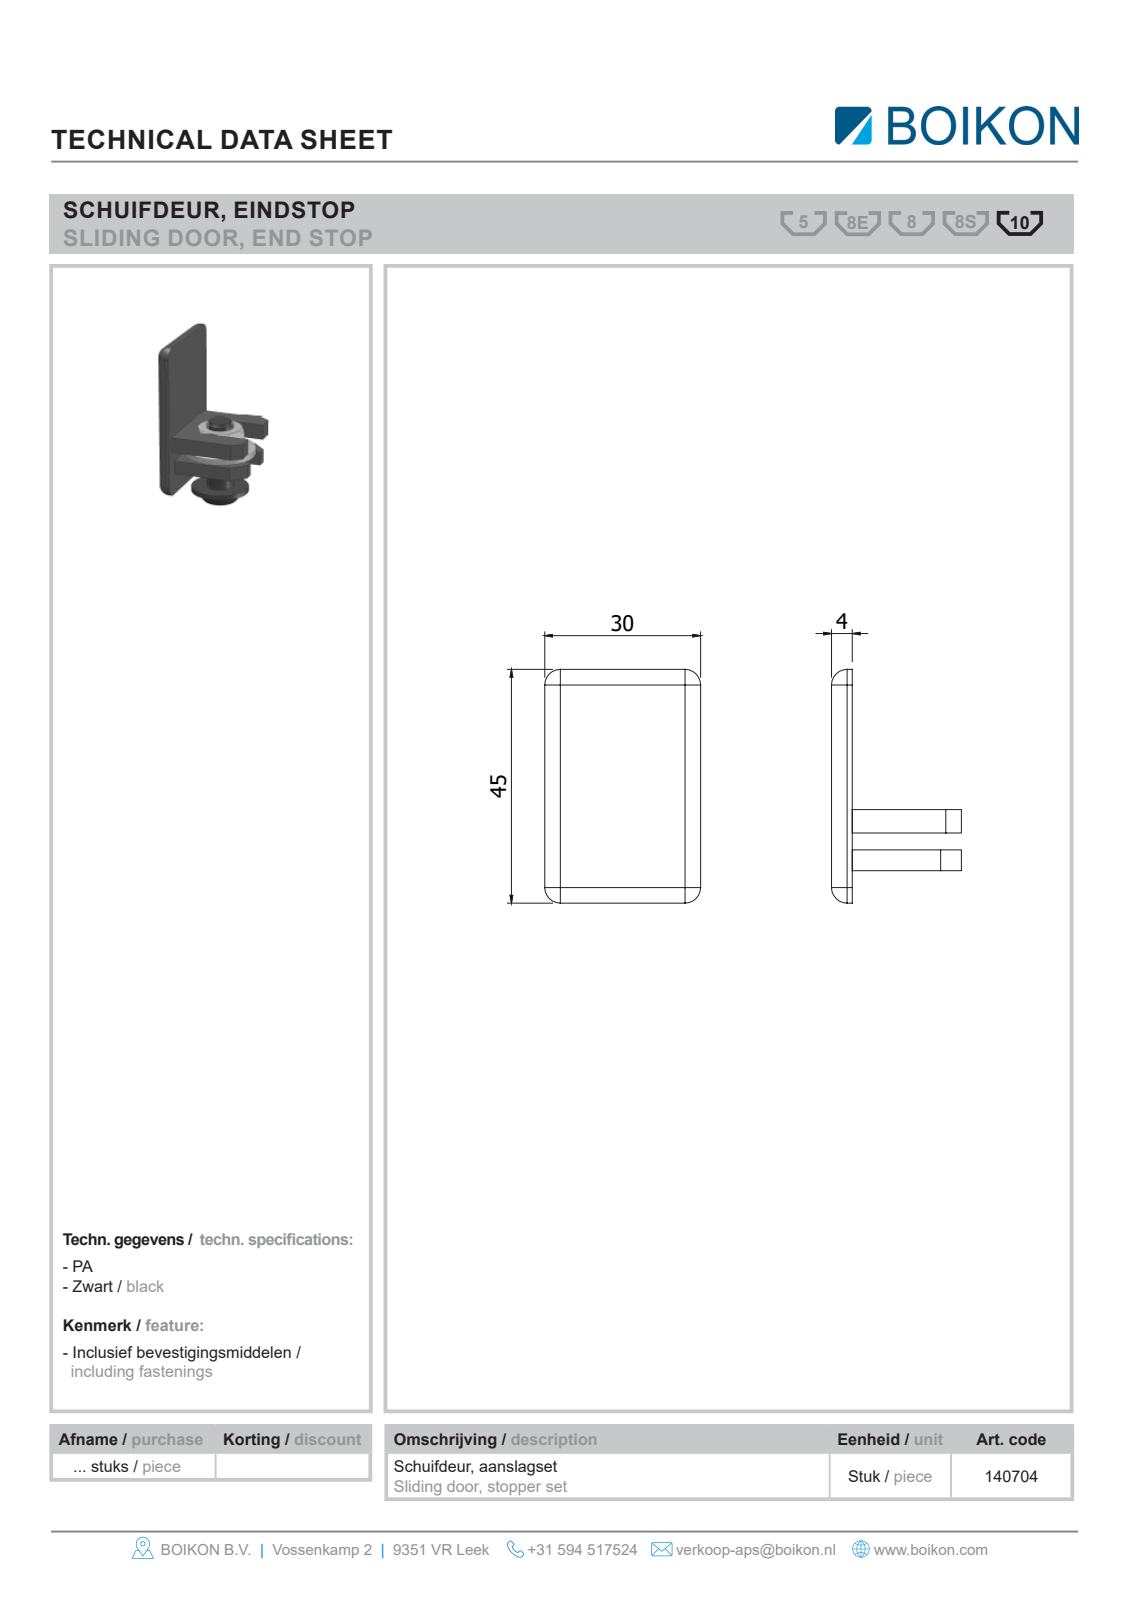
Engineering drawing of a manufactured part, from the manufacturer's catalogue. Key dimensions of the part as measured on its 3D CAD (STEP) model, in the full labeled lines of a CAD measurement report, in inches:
Part name (STEP PRODUCT): Root; 140704Eindstop 30x45C LE01BOIKON; 122000Flensmoer M8BOIKON; 120160Laagbolkopflensschroef M8x20BOIKON
STEP written by: HiCAD 2013 1802.4 Build 509 (AUTOMOTIVE_DESIGN)
Units: inches
Bodies: 3 solids, 81 faces (53 planar, 13 cylindrical, 15 other)
Overall size (bounding box): 1.945 × 1.181 × 0.984
Volume: 0.629 in³ · Surface area: 11.06 in²
Round holes (diameter × count): ⌀0.315 ×1
Round bosses / shafts (diameter × count): ⌀0.827 ×1, ⌀0.669 ×1, ⌀0.255 ×1
Partial cylindrical surfaces — rounded edges, fillets, slot ends (radius × count): R0.118 ×8, R0.167 ×1
Main face-to-face distances: 0.157, 0.177, 0.463, 0.305, 0.285, 0.128, 0.079, 0.531, 0.246, 0.404
